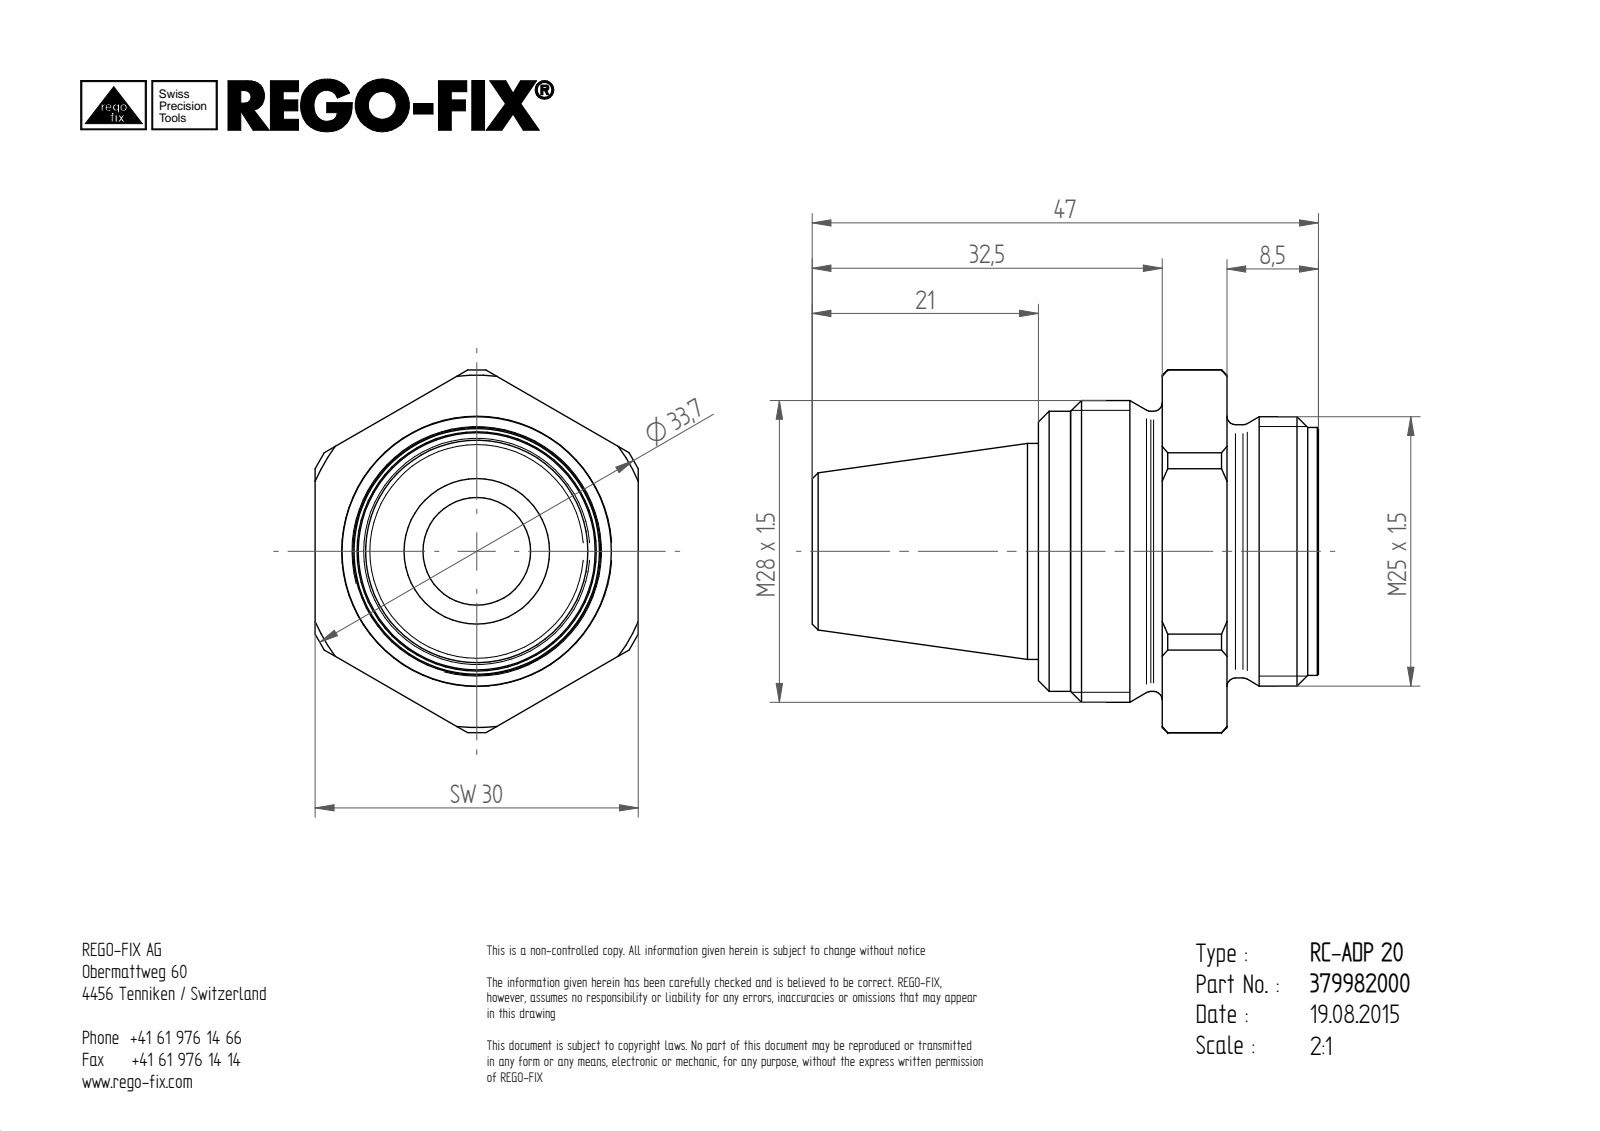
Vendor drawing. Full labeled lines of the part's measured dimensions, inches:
Part name (STEP PRODUCT): 0004341; 0004345-oa0; 0004287-oa1; 0004288-oa2 (+7 more)
STEP written by: Unknown (AUTOMOTIVE_DESIGN)
Units: inches
Bodies: 11 solids, 618 faces (178 planar, 141 cylindrical, 299 other)
Overall size (bounding box): 4.115 × 1.979 × 1.811
Volume: 4.555 in³ · Surface area: 75.88 in²
Round holes (diameter × count): ⌀0.138 ×10, ⌀0.079 ×3, ⌀0.337 ×1, ⌀0.354 ×1, ⌀0.394 ×1, ⌀0.398 ×1, ⌀0.492 ×1, ⌀0.531 ×1, ⌀0.551 ×1, ⌀0.63 ×1, ⌀0.728 ×1, ⌀0.866 ×1
Round bosses / shafts (diameter × count): ⌀1.811 ×1, ⌀1.575 ×1, ⌀1.496 ×1, ⌀1.346 ×1, ⌀1.21 ×1, ⌀1.191 ×1, ⌀1.102 ×1, ⌀1.098 ×1
Partial cylindrical surfaces — rounded edges, fillets, slot ends (radius × count): R0.02 ×8, R0.079 ×4, R0.315 ×2, R0.381 ×2, R0.488 ×2, R0.098 ×1, R0.317 ×1, R0.541 ×1
Main face-to-face distances: 0.024, 0.065, 0.144, 0.079, 0.683, 0.748, 0.604, 0.464, 0.399, 0.787
Hole centre spacings: 0.181, 0.598, 0.331, 0.65
